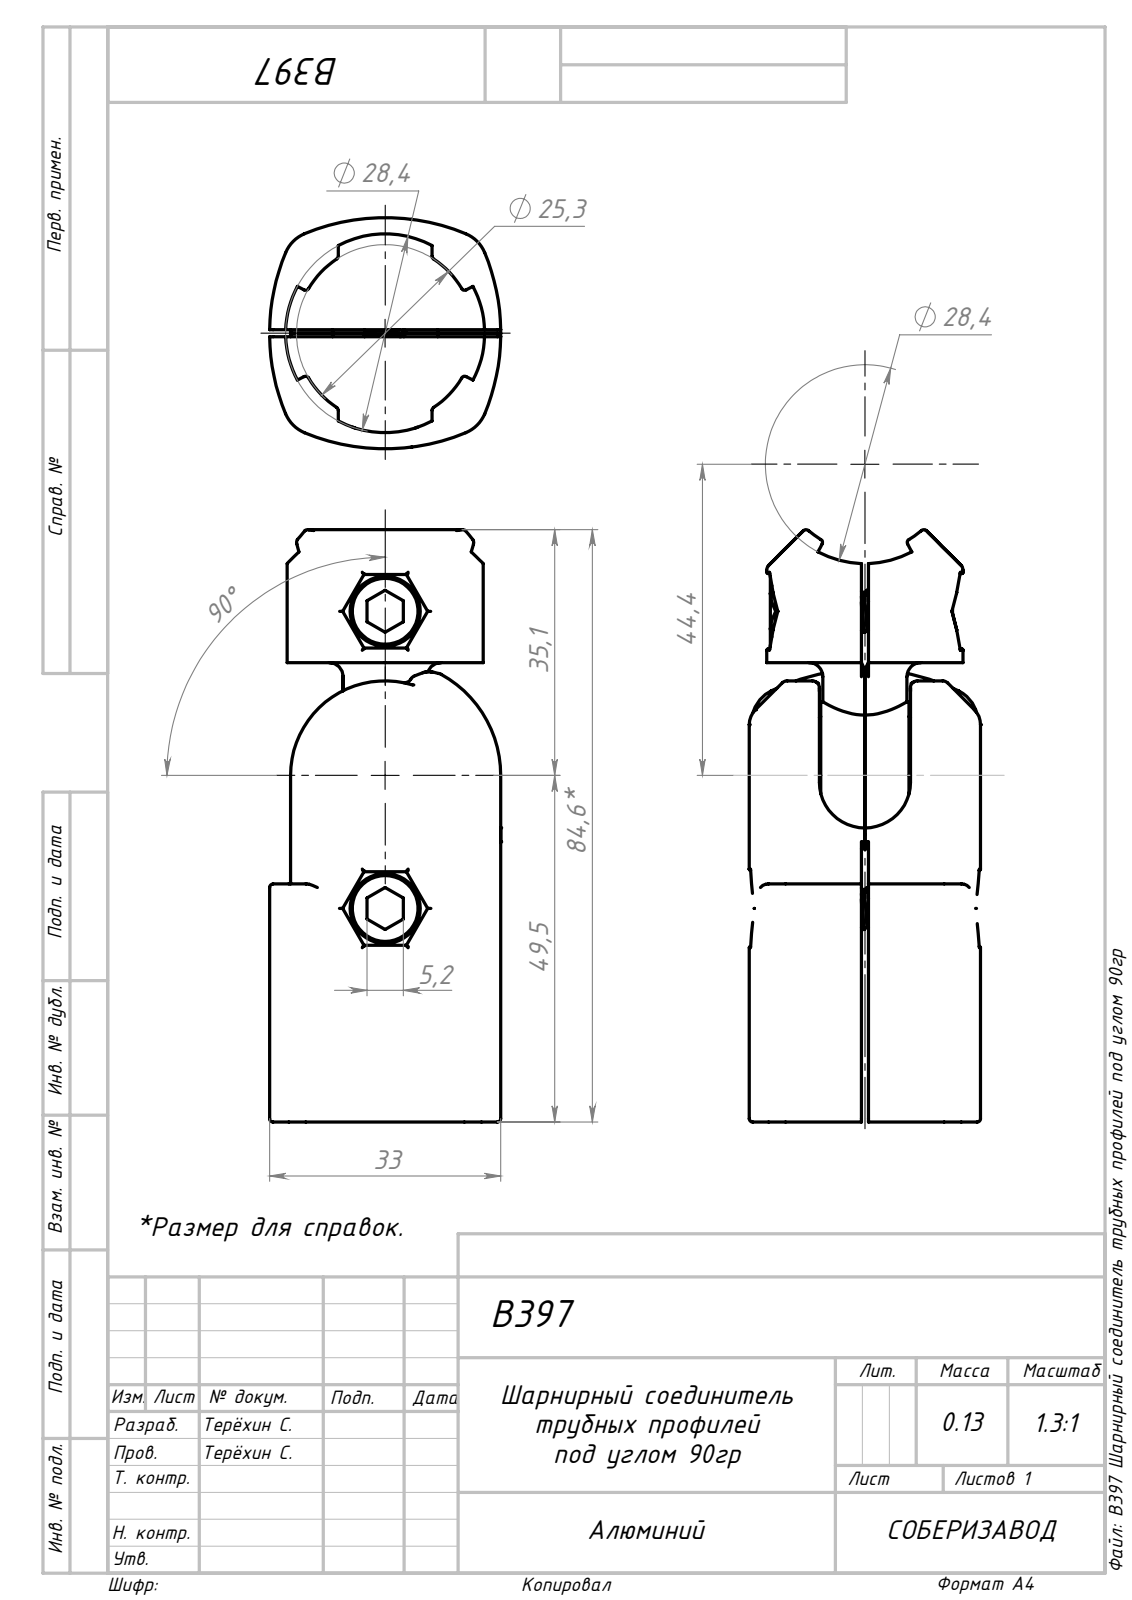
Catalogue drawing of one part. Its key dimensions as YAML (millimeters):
part_name: "B397 Шарнирный соединитель трубных профилей под углом 90гр"
step_written_by: "SolidWorks 2022 (AUTOMOTIVE_DESIGN)"
units: millimeters
bodies: {solids: 8, faces: 745, planar: 214, cylindrical: 232, other: 299}
overall_size: [84.6, 33, 33]
volume: 44848
surface_area: 24893
round_holes:
  - {diameter: 5.2, count: 2}
  - {diameter: 6.5, count: 2}
  - {diameter: 28.4, count: 1}
round_bosses_or_shafts:
  - {diameter: 10, count: 2}
  - {diameter: 6, count: 2}
  - {diameter: 28, count: 1}
  - {diameter: 21, count: 1}
  - {diameter: 12, count: 1}
partial_cylinders:
  - {radius: 0.5, count: 68}
  - {radius: 1, count: 5}
  - {radius: 5, count: 4}
  - {radius: 30, count: 4}
  - {radius: 3, count: 2}
  - {radius: 6.5, count: 2}
  - {radius: 11, count: 1}
  - {radius: 12, count: 1}
face_to_face_distances: [0.5, 1, 7, 6, 6.5, 13, 10.28, 10, 21.22, 3]
hole_center_spacings: [42.44]
